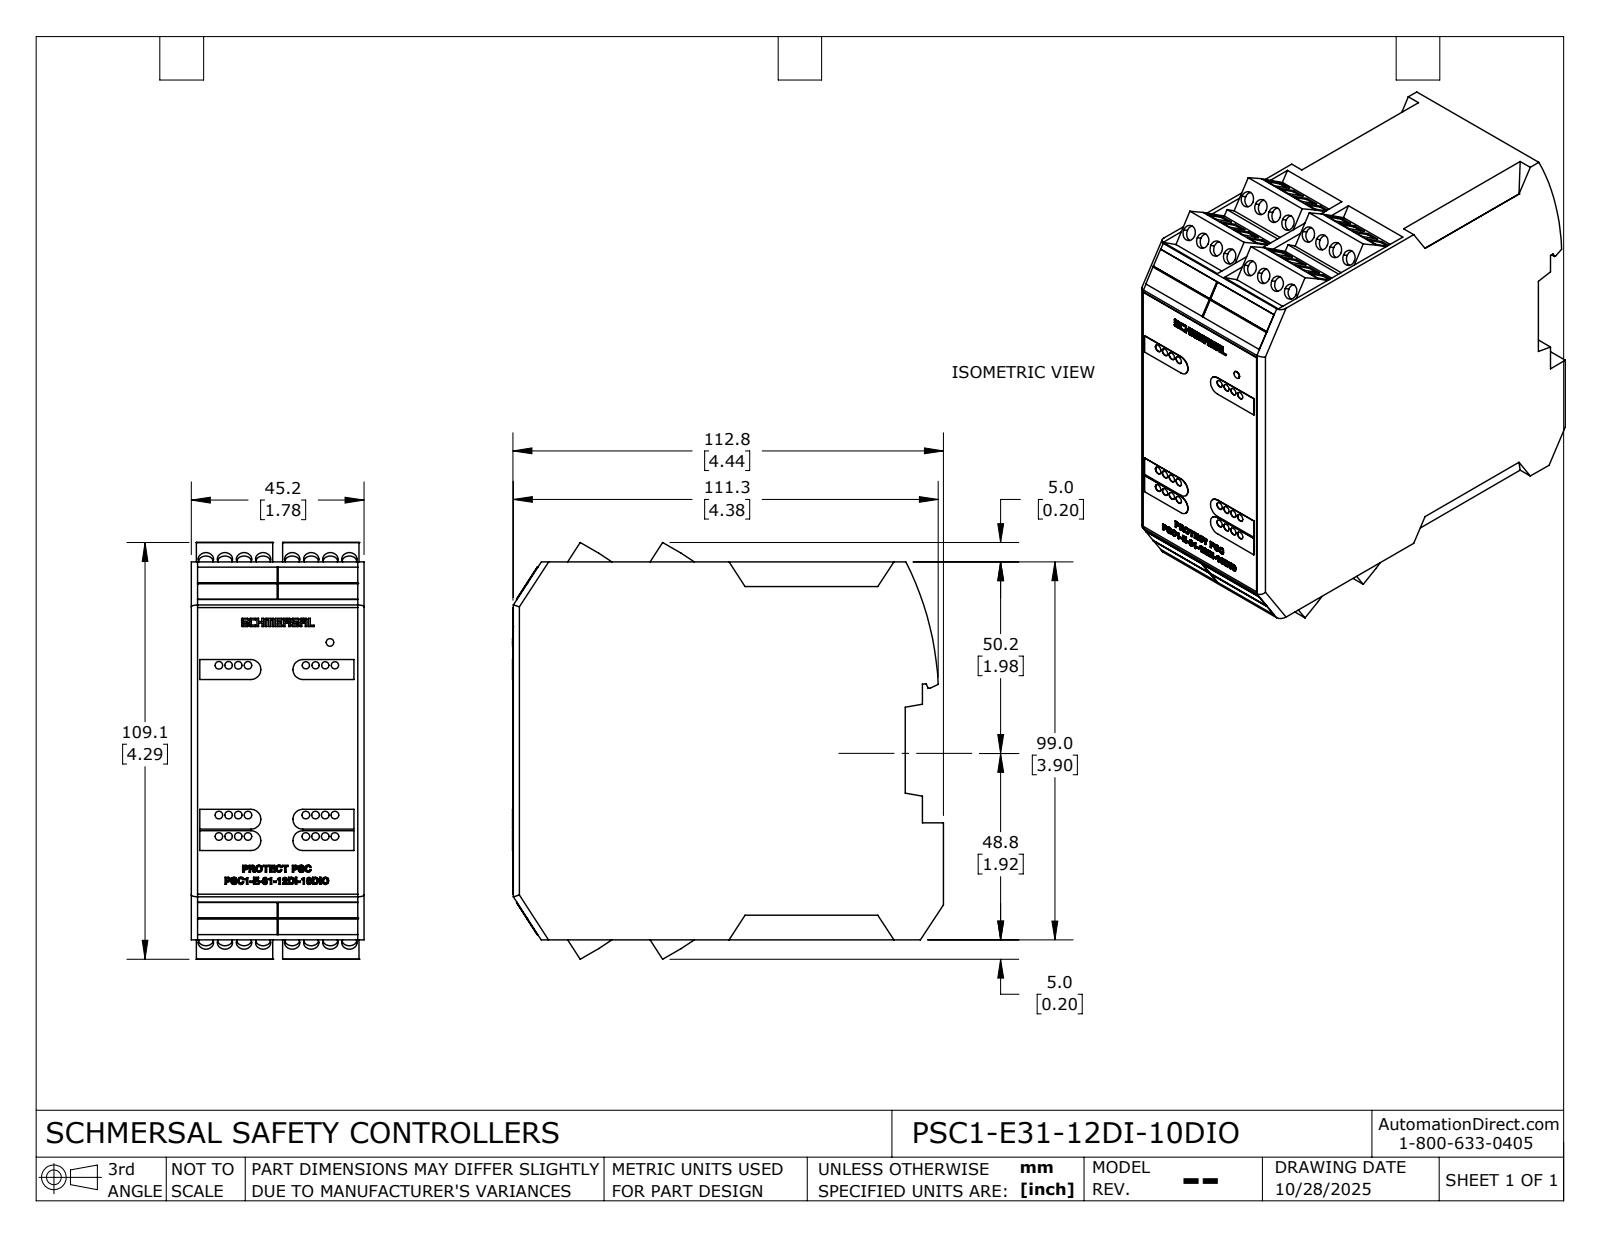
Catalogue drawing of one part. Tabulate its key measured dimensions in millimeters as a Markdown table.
| quantity | value |
| --- | --- |
| part name | PSC1-E31-12DI-10DIO |
| STEP written by | SolidWorks 2024 (AUTOMOTIVE_DESIGN) |
| units | millimeters |
| bodies | 1 solid, 1120 faces (588 planar, 133 cylindrical, 399 other) |
| overall size | 112.85 × 109.09 × 45.2 |
| volume | 478 320 mm³ |
| surface area | 46 456 mm² |
| round holes (diameter × count) | 4 × 32, 2 × 20, 1.89 × 4 |
| round bosses / shafts (diameter × count) | 2 × 1 |
| partial cylindrical surfaces (radius × count) | 1.6 × 6, 2.6 × 6, 80 × 1 |
| main face-to-face distances | 45.2, 22.6, 20.05, 99, 20, 1.3, 21.3, 23.9, 43.9, 20.1 |
| hole center spacings | 5, 12.78, 2.54, 10, 11.76, 15.44, 22.6, 25.48 |
